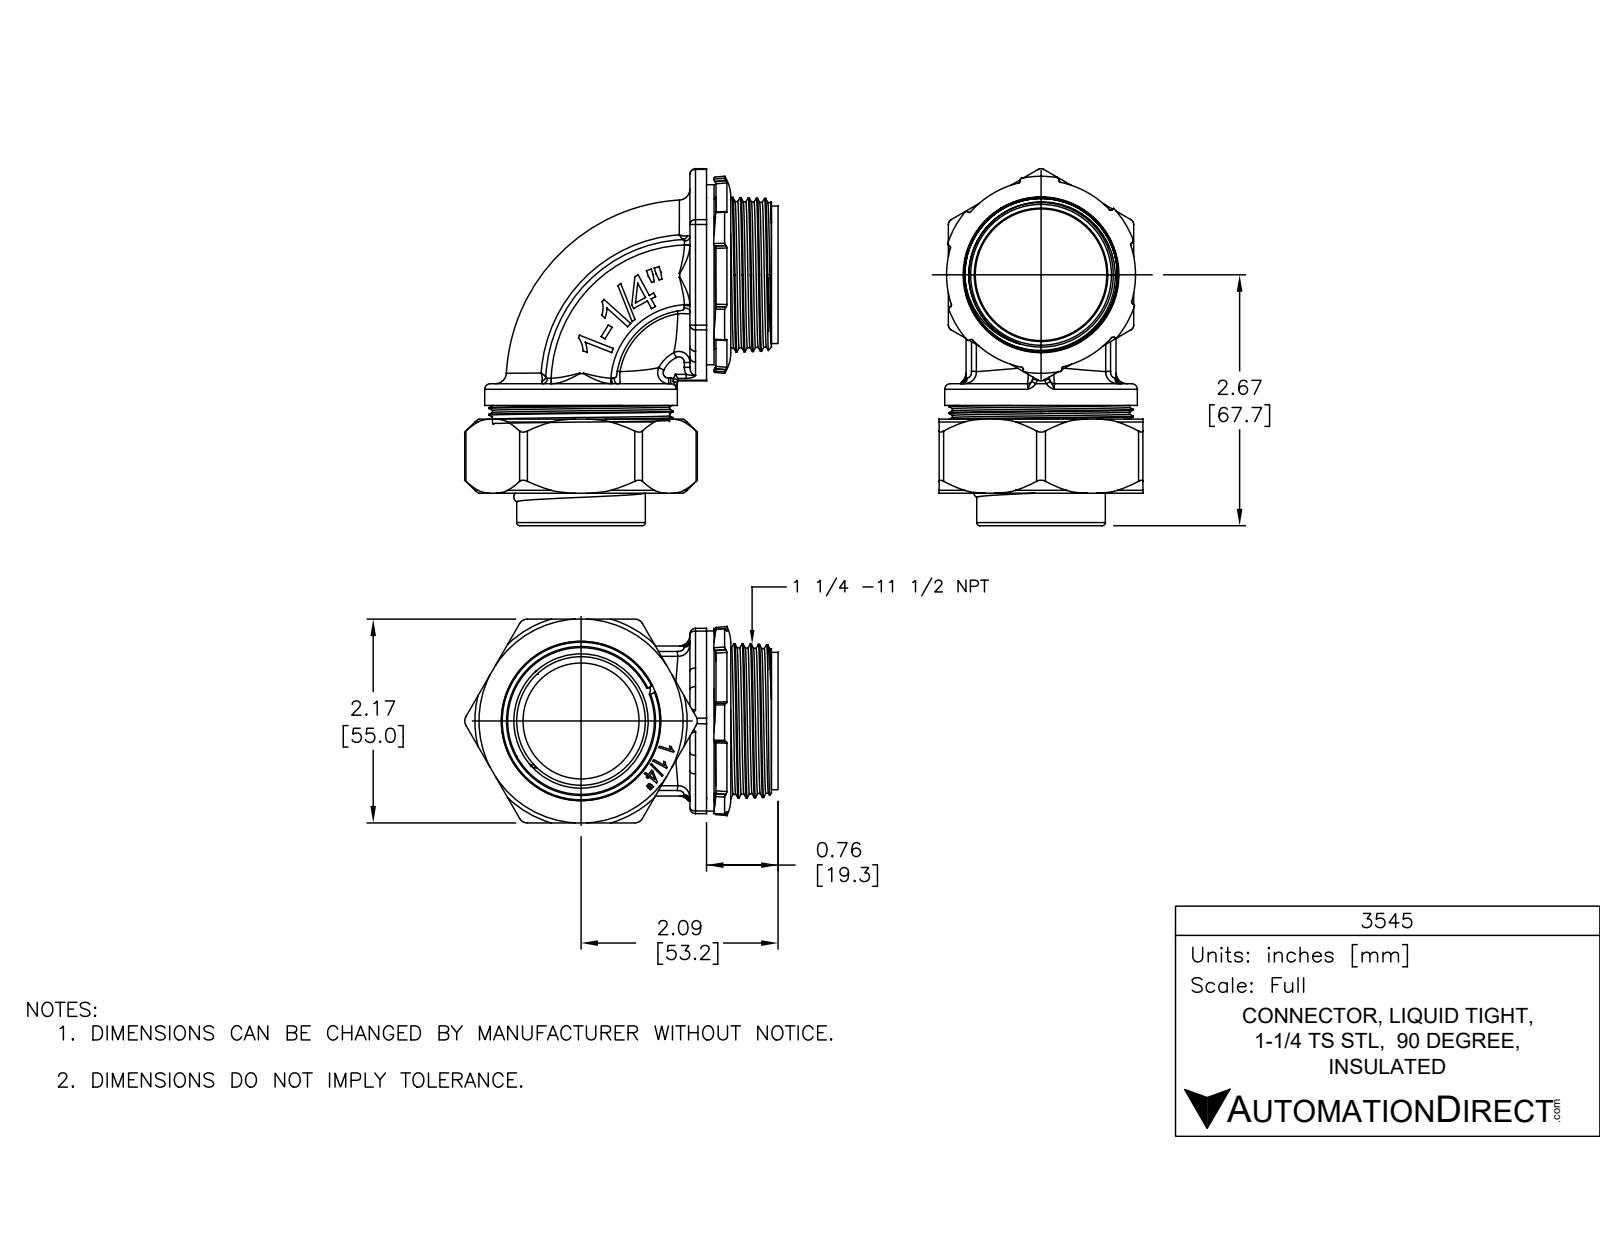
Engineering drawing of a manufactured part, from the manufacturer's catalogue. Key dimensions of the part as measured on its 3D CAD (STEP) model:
Part name (STEP PRODUCT): 3545
STEP written by: SolidWorks 2018 (AUTOMOTIVE_DESIGN)
Units: inches
Bodies: 7 solids, 687 faces (274 planar, 129 cylindrical, 284 other)
Overall size (bounding box): 3.794 × 3.329 × 2.165
Volume: 3.863 in³ · Surface area: 91.22 in²
Round holes (diameter × count): ⌀1.398 ×2, ⌀0.182 ×1, ⌀1.232 ×1, ⌀1.26 ×1, ⌀1.3 ×1, ⌀1.418 ×1, ⌀1.555 ×1, ⌀1.638 ×1, ⌀1.666 ×1, ⌀1.693 ×1, ⌀1.76 ×1, ⌀1.909 ×1
Round bosses / shafts (diameter × count): ⌀2.047 ×1, ⌀1.953 ×1, ⌀1.913 ×1, ⌀1.87 ×1, ⌀1.732 ×1, ⌀1.465 ×1, ⌀1.366 ×1, ⌀1.298 ×1
Partial cylindrical surfaces — rounded edges, fillets, slot ends (radius × count): R0.059 ×16, R0.012 ×8, R0.094 ×6, R0.004 ×2, R0.049 ×2, R0.052 ×2, R0.006 ×1, R0.015 ×1
Main face-to-face distances: 2.165, 0.285, 1.88, 0.932, 1.594, 0.079, 0.787, 0.376, 0.76, 0.681
Hole centre spacings: 0.965
